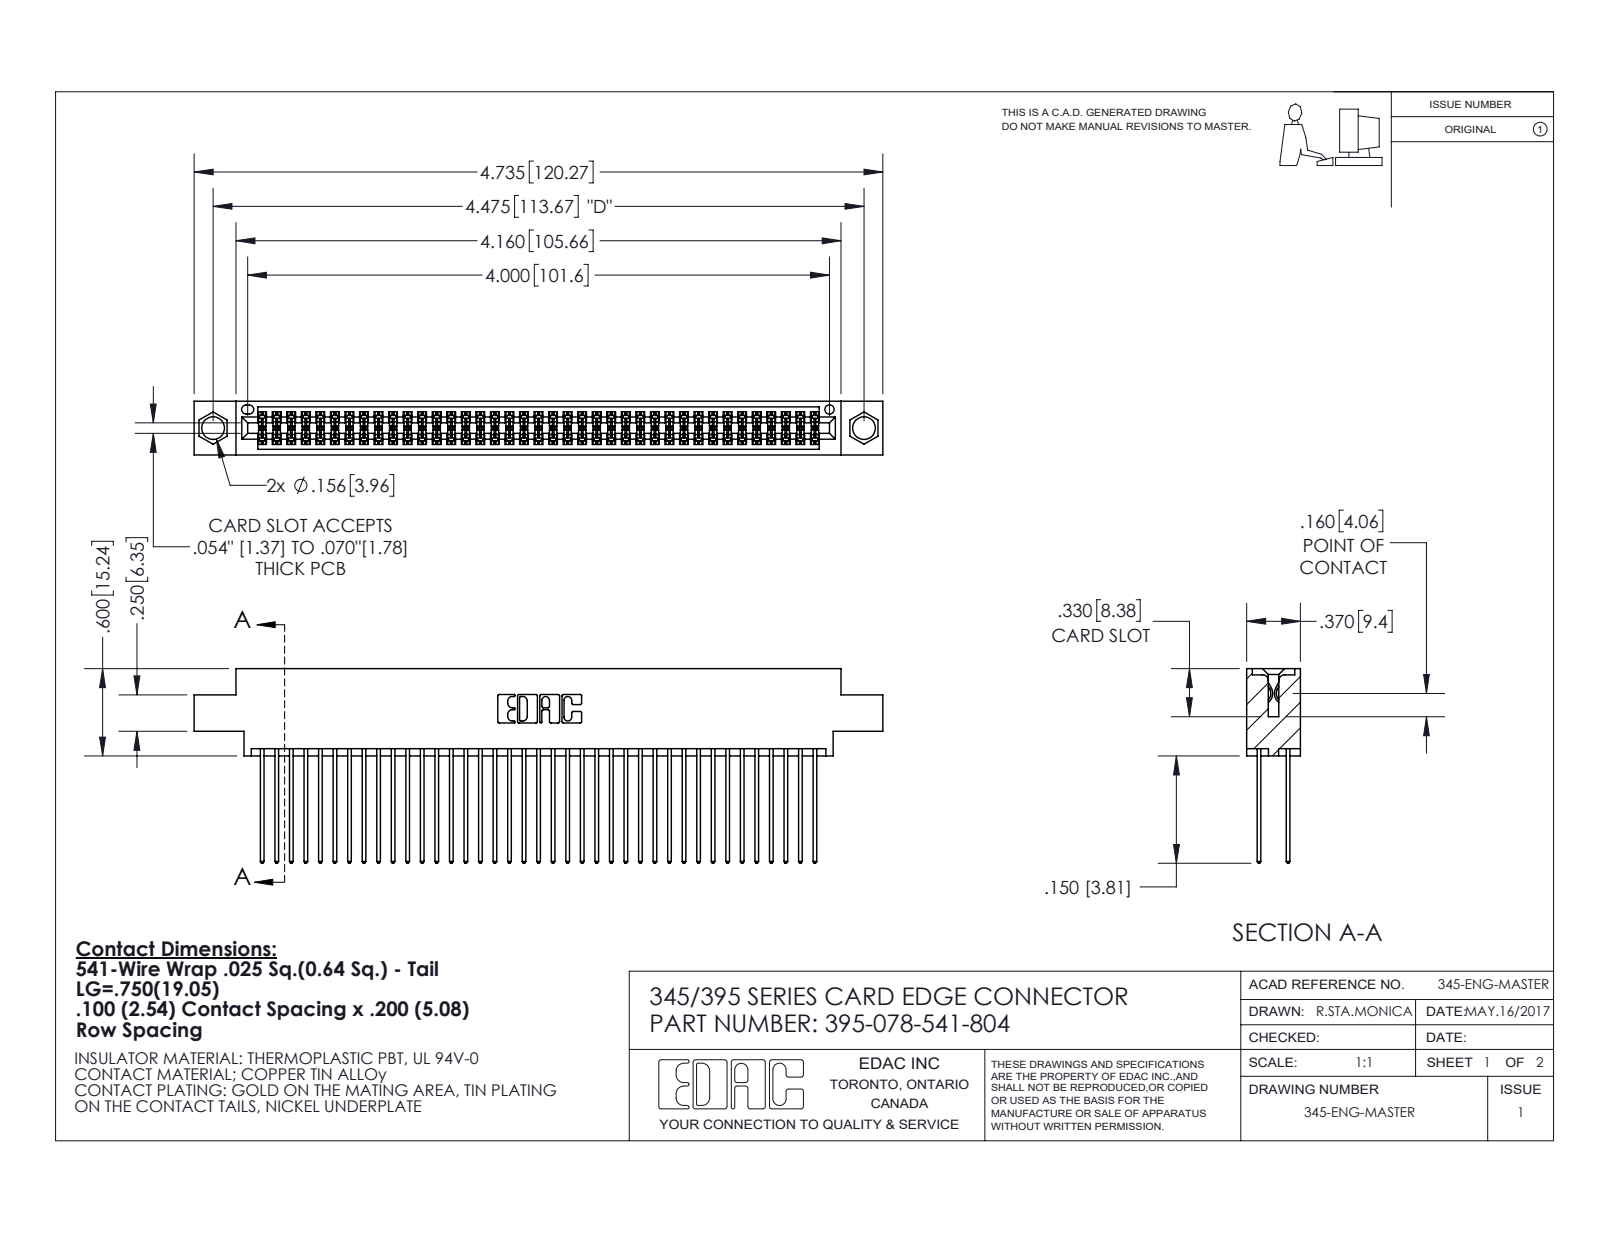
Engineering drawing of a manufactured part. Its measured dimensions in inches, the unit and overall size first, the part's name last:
Units: inches
Overall size (bounding box): 4.735 × 1.337 × 0.37
Round holes (diameter × count): ⌀0.156 ×2, ⌀0.064 ×1
Partial cylindrical surfaces — rounded edges, fillets, slot ends (radius × count): R0.006 ×117, R0.01 ×78, R0.01 ×22, R0.007 ×6, R0.031 ×6, R0.026 ×3, R0.014 ×2, R0.019 ×2
Main face-to-face distances: 0.072, 0.298, 0.2, 0.098, 0.272, 0.025, 0.37, 0.225, 0.175, 0.149
Hole centre spacings: 0.27, 4.239, 4.475
Volume: 0.725 in³ · Surface area: 30.39 in²
Bodies: 79 solids, 4044 faces (2672 planar, 1372 cylindrical, 0 other)
Part name (STEP PRODUCT): 345-292-001_345-293-141; 345 Part_0.170 Offset - 0.156 Dia-TI; 395-078-541-804
STEP written by: SolidWorks 2020 (CONFIG_CONTROL_DESIGN)
